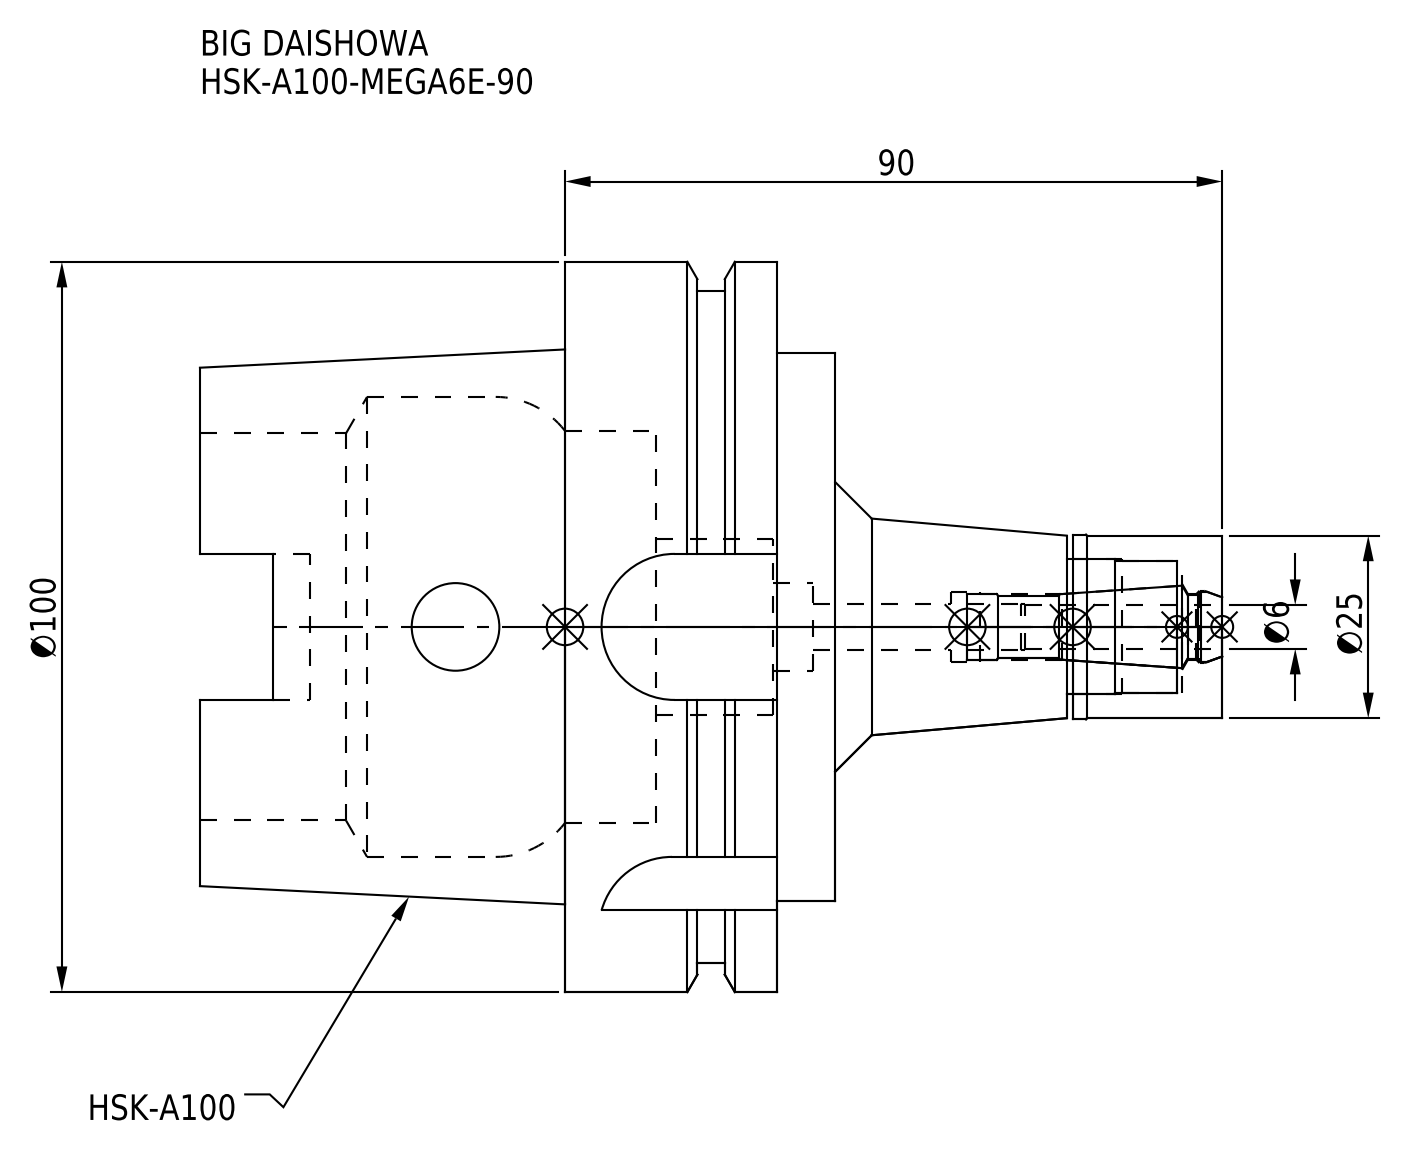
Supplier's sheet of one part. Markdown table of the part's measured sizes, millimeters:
| quantity | value |
| --- | --- |
| part name | HSK-A100-MEGA6E-90_1.stp; HA100ME06090-060_ASM.stp; DXF_TEMP_ASSY_ASM_4_ASM.stp; MEN6_1.stp (+3 more) |
| STEP written by | SolidWorks 2019 (CONFIG_CONTROL_DESIGN) |
| units | millimeters |
| bodies | 2 solids, 126 faces (42 planar, 56 cylindrical, 28 other) |
| overall size | 140 × 100 × 100 |
| volume | 315 670 mm³ |
| surface area | 60 028 mm² |
| round holes (diameter × count) | 12 × 2, 6.4 × 1, 9 × 1, 9.6 × 1, 9.9 × 1, 18 × 1, 18.5 × 1, 24 × 1, 53 × 1, 53.8 × 1, 63 × 1 |
| round bosses / shafts (diameter × count) | 100 × 1, 92 × 1, 75 × 1, 25.3 × 1, 25 × 1 |
| partial cylindrical surfaces (radius × count) | 4.88 × 4, 10 × 4 |
| main face-to-face distances | 29, 37, 8, 24.55, 16.55, 12.45, 87, 79, 62.45, 50 |
